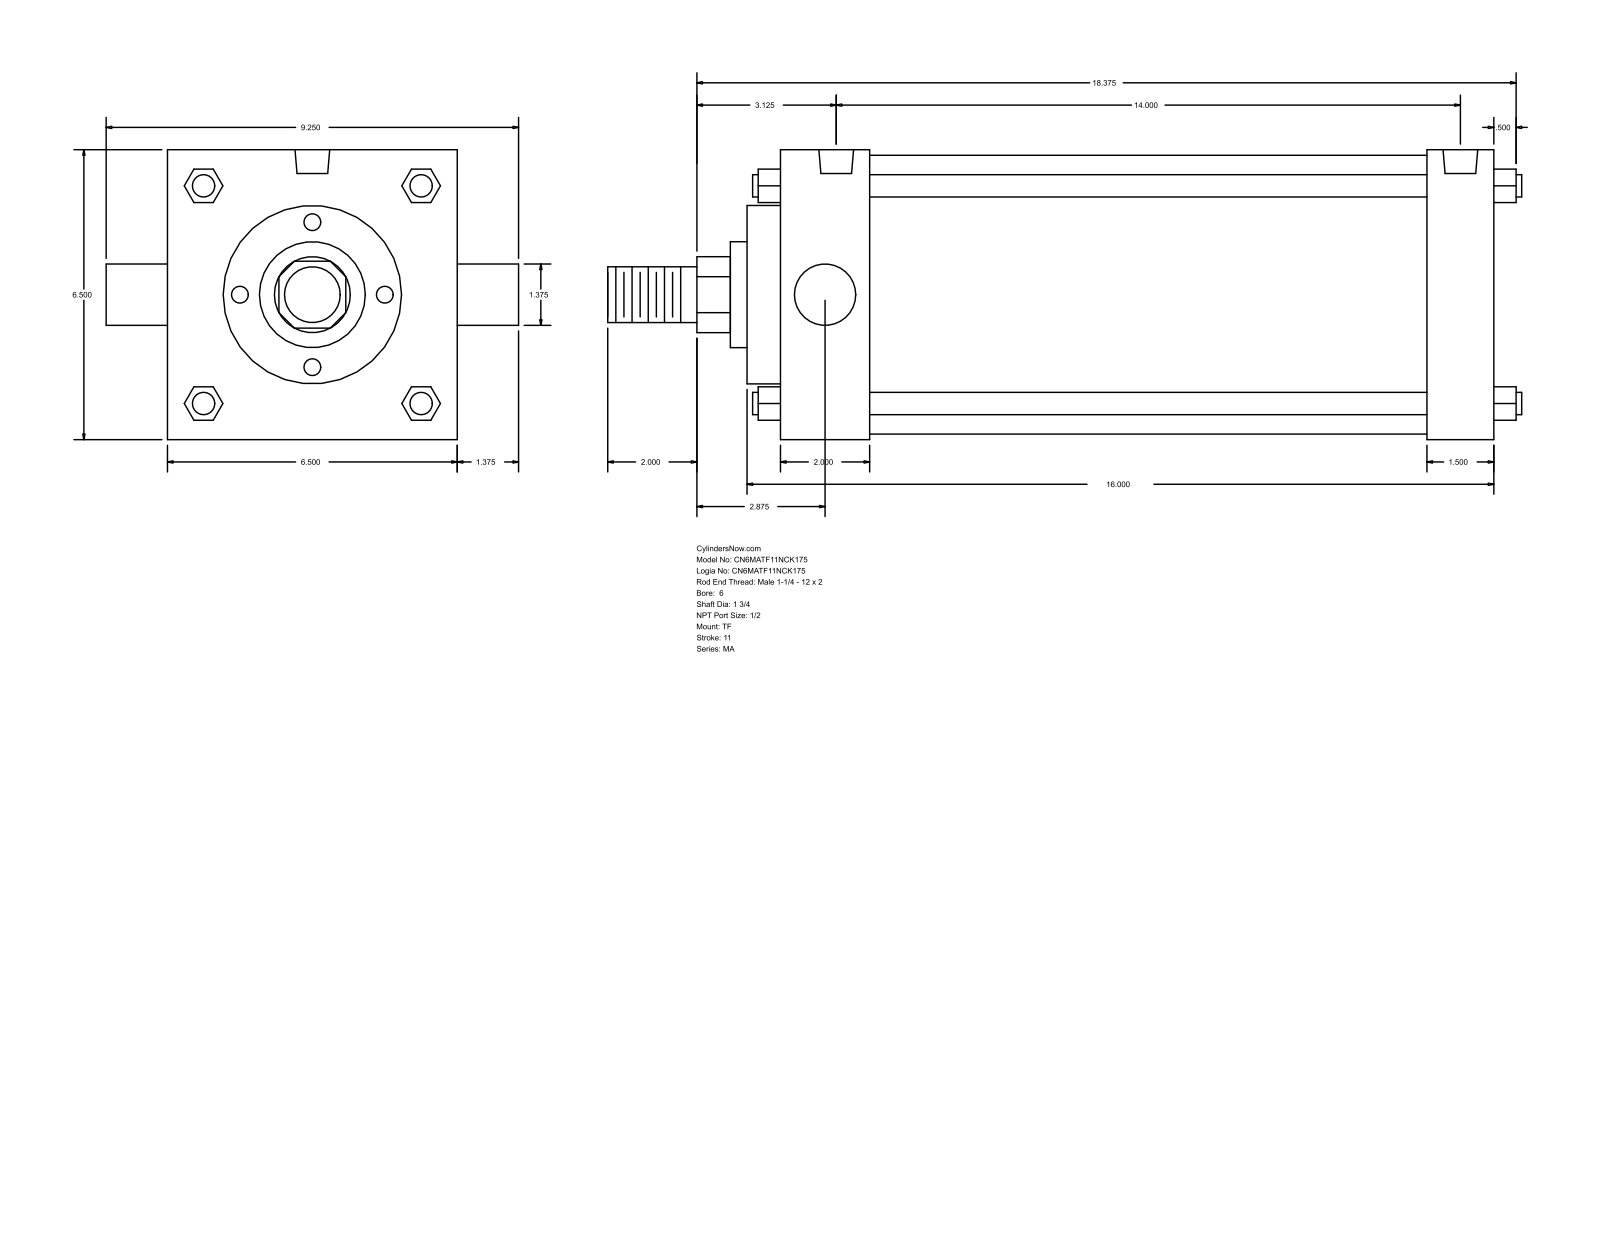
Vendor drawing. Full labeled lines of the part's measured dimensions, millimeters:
Part name (STEP PRODUCT): MA_TF__0600_1.75
STEP written by: GSSL Pune (CONFIG_CONTROL_DESIGN)
Units: millimetres
Bodies: 0 solids, 122 faces (93 planar, 29 cylindrical, 0 other)
Overall size (bounding box): 520.7 × 234.95 × 165.1
Round holes (diameter × count): ⌀17.46 ×3, ⌀19.77 ×2
Round bosses / shafts (diameter × count): ⌀12.7 ×4, ⌀158.75 ×1, ⌀101.6 ×1, ⌀60.33 ×1, ⌀44.45 ×1, ⌀34.92 ×1, ⌀31.75 ×1
Partial cylindrical surfaces — rounded edges, fillets, slot ends (radius × count): R21.63 ×1
Main face-to-face distances: 165.1, 406.4, 19.05, 50.8, 368.31, 355.6, 317.51, 38.09, 69.85, 387.36
Hole centre spacings: 355.6
